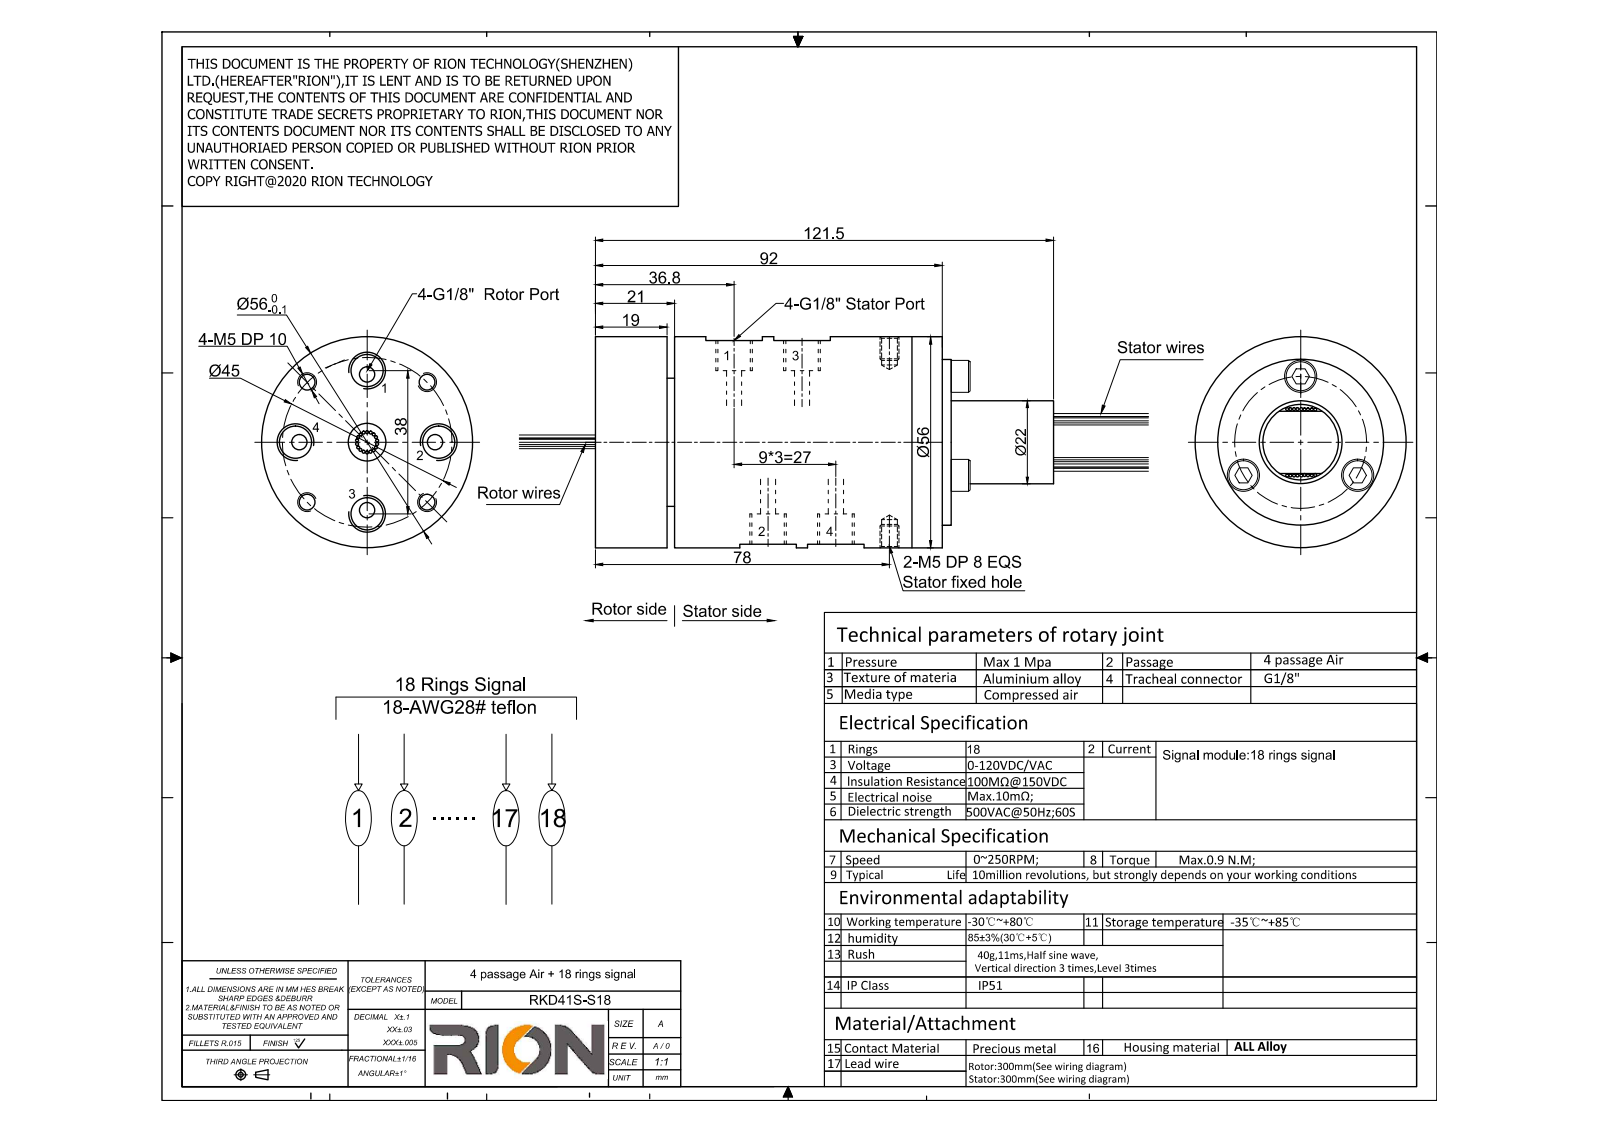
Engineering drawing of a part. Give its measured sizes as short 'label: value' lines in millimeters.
name: RKD41S-S18
written by: SolidWorks 2014 (CONFIG_CONTROL_DESIGN)
unit: mm
bodies: 1 solid, 269 faces (94 planar, 141 cylindrical, 34 other)
size: 161.4 × 56 × 56
volume: 231 310 mm³; area: 32 515 mm²
holes: 9× ⌀4, 8× ⌀8.8, 5× ⌀4.2, 1× ⌀9.5, 1× ⌀20
bosses: 36× ⌀0.8, 3× ⌀8.5, 1× ⌀56, 1× ⌀44, 1× ⌀34, 1× ⌀22, 1× ⌀19.9
face distances: 19, 21, 2, 94.4, 75.4, 73.4, 92, 73, 71, 2.4
hole spacings: 16.05, 16.21, 26.17, 37.46, 38.36, 18, 1, 19
